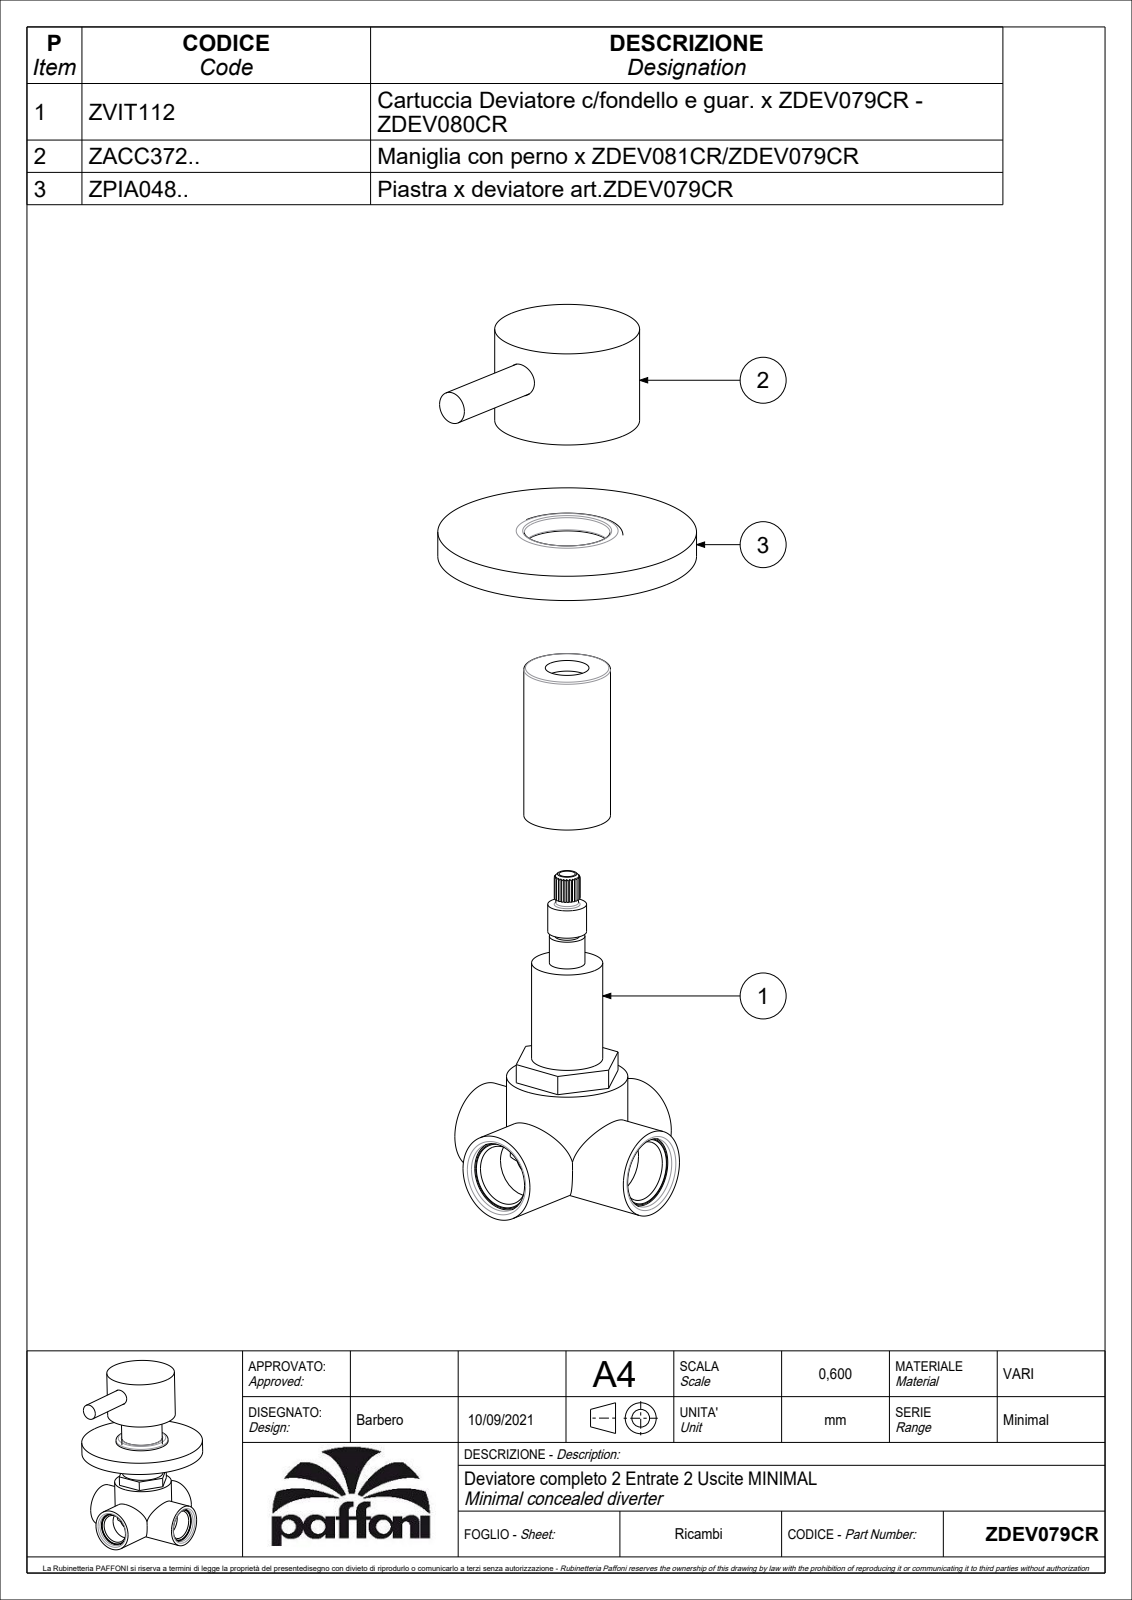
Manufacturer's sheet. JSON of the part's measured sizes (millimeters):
{"part_name": "ZDEV079CR", "step_written_by": "CREO PARAMETRIC BY PTC INC, 2020044 (CONFIG_CONTROL_DESIGN)", "units": "millimeters", "bodies": {"solids": 1, "faces": 320, "planar": 180, "cylindrical": 50, "other": 90}, "overall_size": [95.4, 80, 62.29], "volume_mm3": 61587, "surface_area_mm2": 32538, "round_holes": [[3.3, 1], [4.2, 1], [4.5, 1], [5, 1], [7, 1], [9, 1], [10.2, 1], [13.5, 1], [20.7, 1], [24, 1], [39, 1], [76, 1]], "round_bosses_or_shafts": [[80, 1], [44.8, 1], [34.5, 1], [31, 1], [27, 1], [22, 1], [12, 1], [11, 1]], "face_to_face_distances": [2, 41.4, 39.4, 6, 8, 47.4, 1, 3.5, 28.5, 39]}
